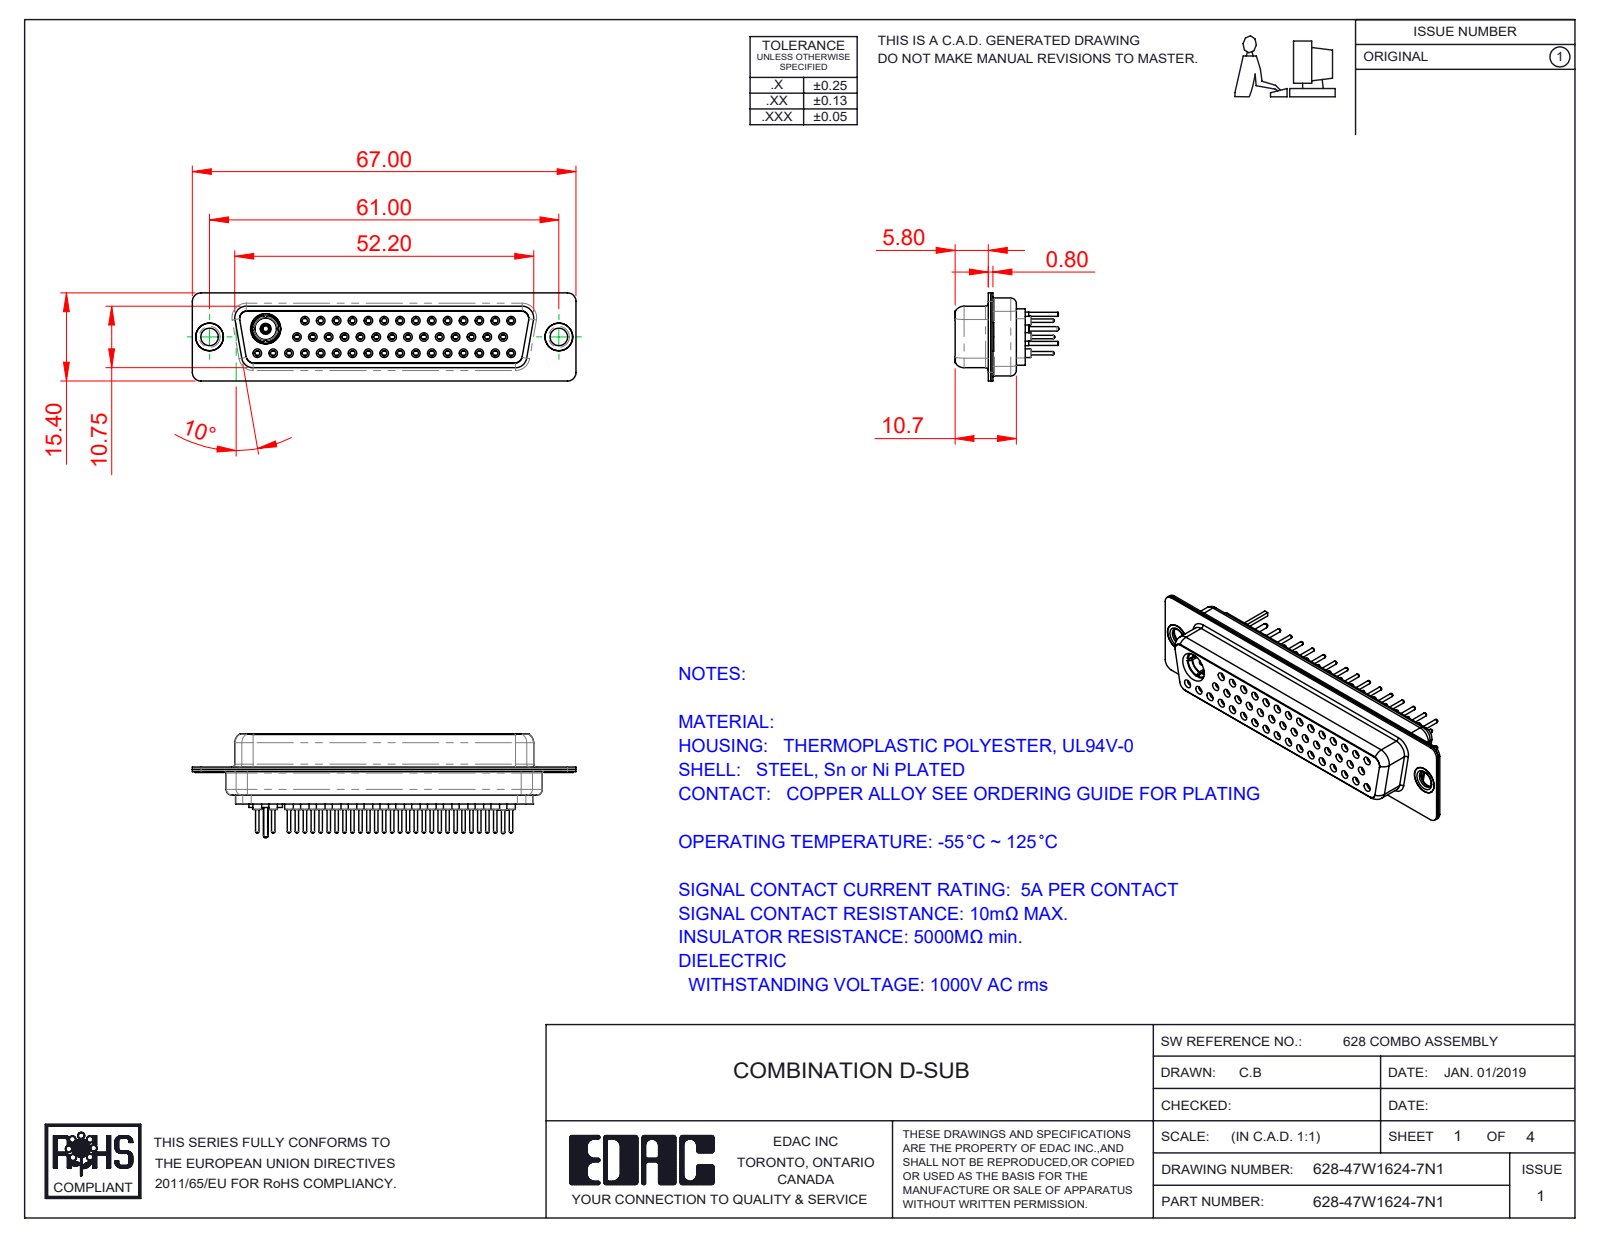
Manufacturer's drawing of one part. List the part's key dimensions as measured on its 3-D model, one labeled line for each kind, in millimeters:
Part name (STEP PRODUCT): 628-47W1624-7N1; Co-Ax Plug Assy_St; Co-Ax Plug_Straight PC Tail; Insulator Pin_Straight PC Tail (+8 more)
STEP written by: SolidWorks 2016 (CONFIG_CONTROL_DESIGN)
Units: millimetres
Bodies: 55 solids, 2897 faces (811 planar, 1032 cylindrical, 1054 other)
Overall size (bounding box): 67 × 18.15 × 15.4
Volume: 6 967 mm³ · Surface area: 14 734 mm²
Round holes (diameter × count): ⌀1.1 ×47, ⌀1.5 ×46, ⌀0.9 ×45, ⌀2 ×45, ⌀1.6 ×31, ⌀1.7 ×14, ⌀4.85 ×3, ⌀3.05 ×2, ⌀4 ×2, ⌀4.05 ×2, ⌀2.83 ×1, ⌀3.3 ×1
Round bosses / shafts (diameter × count): ⌀2.2 ×46, ⌀0.6 ×46, ⌀1.6 ×15, ⌀5 ×3, ⌀4.95 ×2, ⌀4.8 ×2, ⌀3.55 ×2, ⌀5.85 ×1
Partial cylindrical surfaces — rounded edges, fillets, slot ends (radius × count): R1.5 ×16, R1.35 ×12, R2 ×12, R1.6 ×8, R0.25 ×4, R0.5 ×4, R0.6 ×4, R0.65 ×4
Main face-to-face distances: 0.4, 6.45, 6.05, 11.33, 1.87, 12.25, 6.2, 5.8, 10.35, 10.93
Hole centre spacings: 3.16, 2.77, 5.54, 8.31, 11.08, 13.85, 16.62, 19.39
